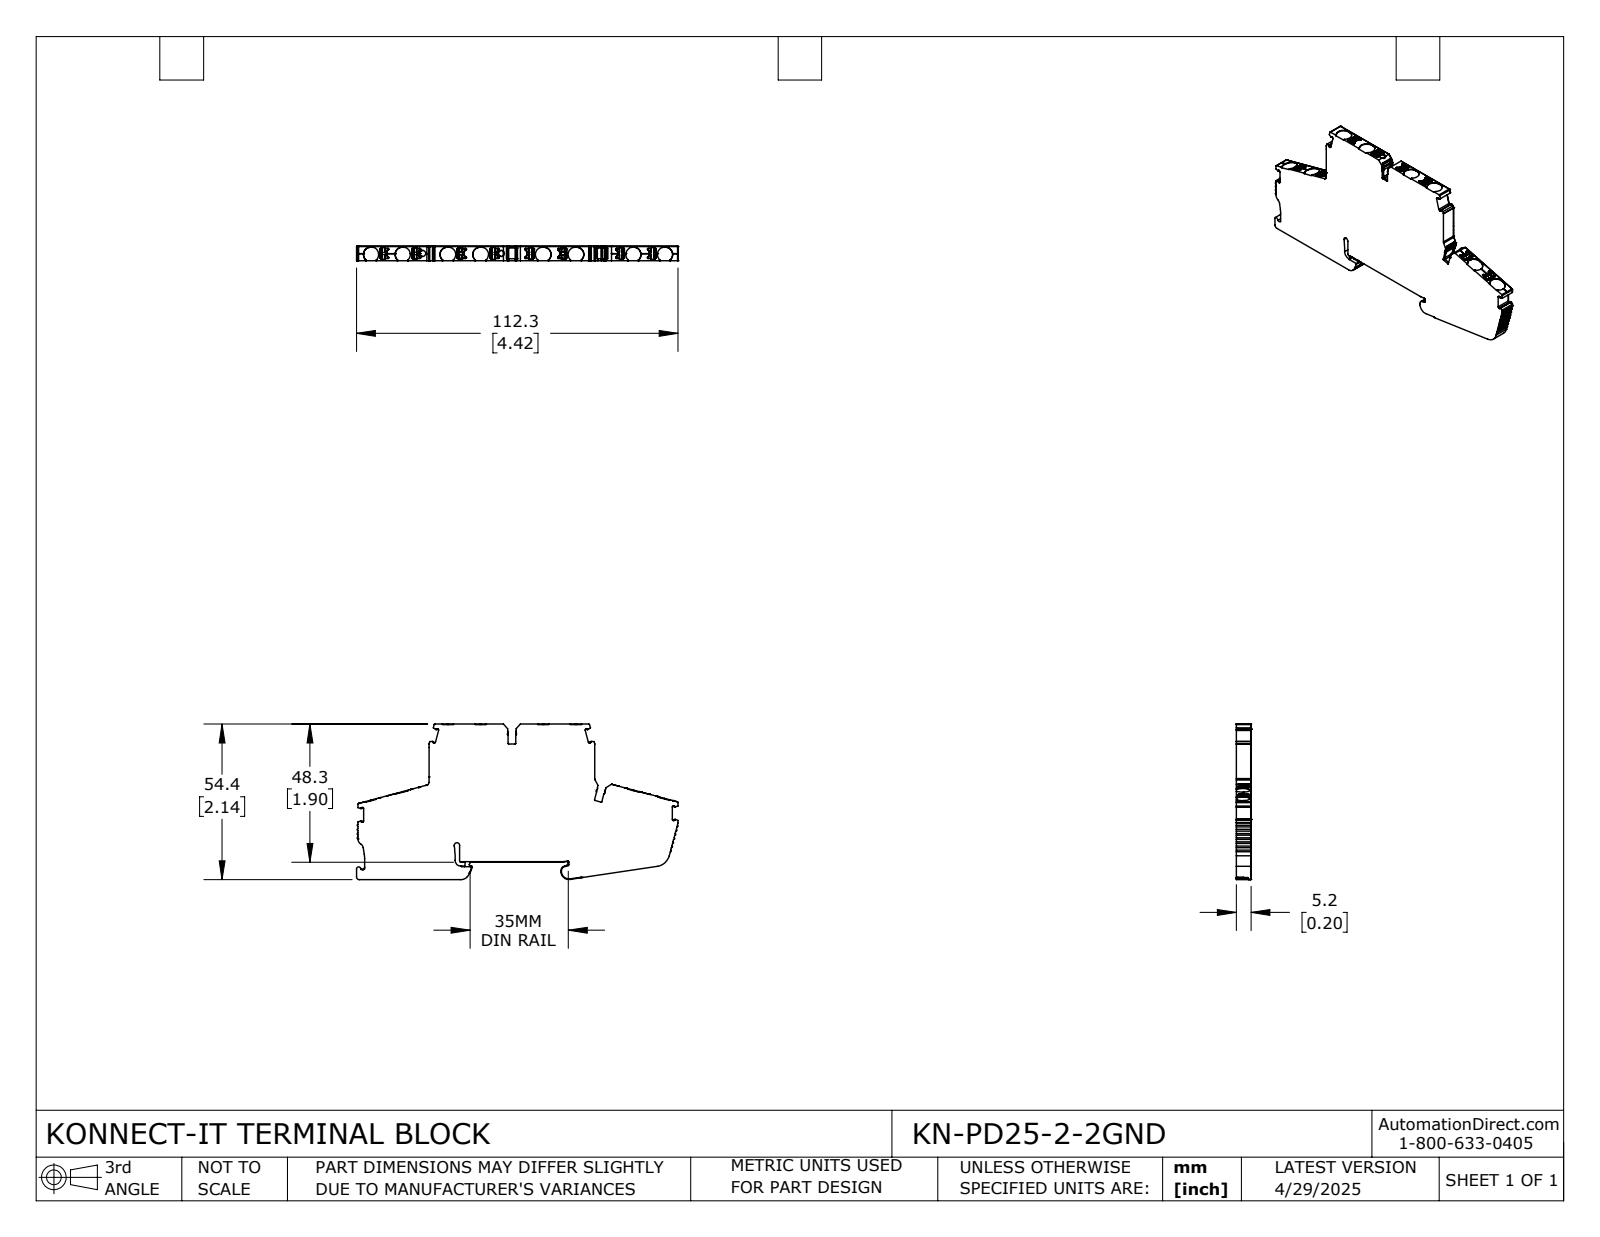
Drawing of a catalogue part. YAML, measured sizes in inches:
part_name: "KN-PD25-2-2GND"
step_written_by: "SolidWorks 2024 (CONFIG_CONTROL_DESIGN)"
units: inches
bodies: {solids: 1, faces: 1151, planar: 562, cylindrical: 451, other: 138}
overall_size: [4.422, 2.141, 0.203]
volume: 1.353
surface_area: 16.68
round_holes:
  - {diameter: 0.083, count: 2}
partial_cylinders:
  - {radius: 0.008, count: 97}
  - {radius: 0.012, count: 43}
  - {radius: 0.004, count: 37}
  - {radius: 0.006, count: 32}
  - {radius: 0.016, count: 18}
  - {radius: 0.1, count: 16}
  - {radius: 0.02, count: 15}
  - {radius: 0.039, count: 9}
face_to_face_distances: [0.203, 1.893, 2.141, 2.133, 0.24, 1.9, 0.248, 1.885, 2.279, 0.079]
